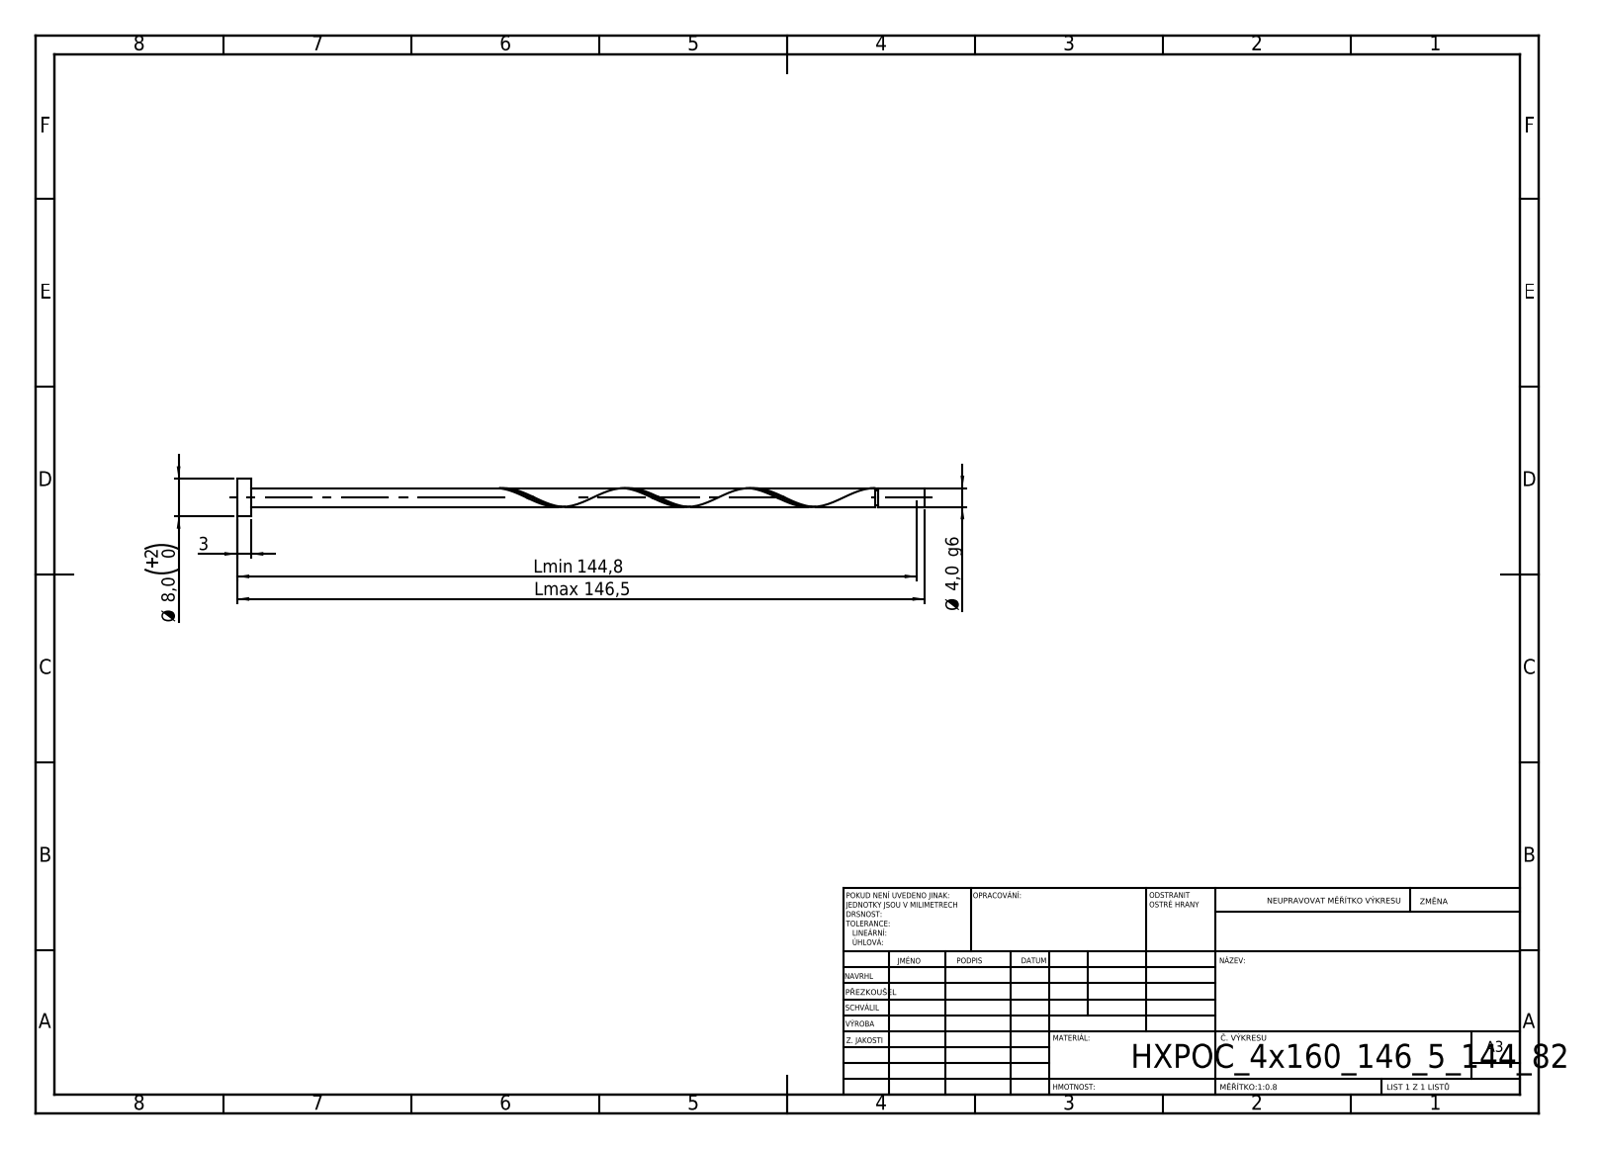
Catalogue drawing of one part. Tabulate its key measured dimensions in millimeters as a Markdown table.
| quantity | value |
| --- | --- |
| STEP written by | SolidWorks 2019 (CONFIG_CONTROL_DESIGN) |
| units | millimeters |
| bodies | 1 solid, 21 faces (6 planar, 14 cylindrical, 1 other) |
| overall size | 146.5 × 8 × 8 |
| volume | 1 931 mm³ |
| surface area | 2 021 mm² |
| round bosses / shafts (diameter × count) | 8 × 1, 4 × 1, 3.2 × 1 |
| main face-to-face distances | 3, 146.5, 143.5, 136.64, 133.64, 9.86, 135.84, 132.84, 0.8, 10.66 |
